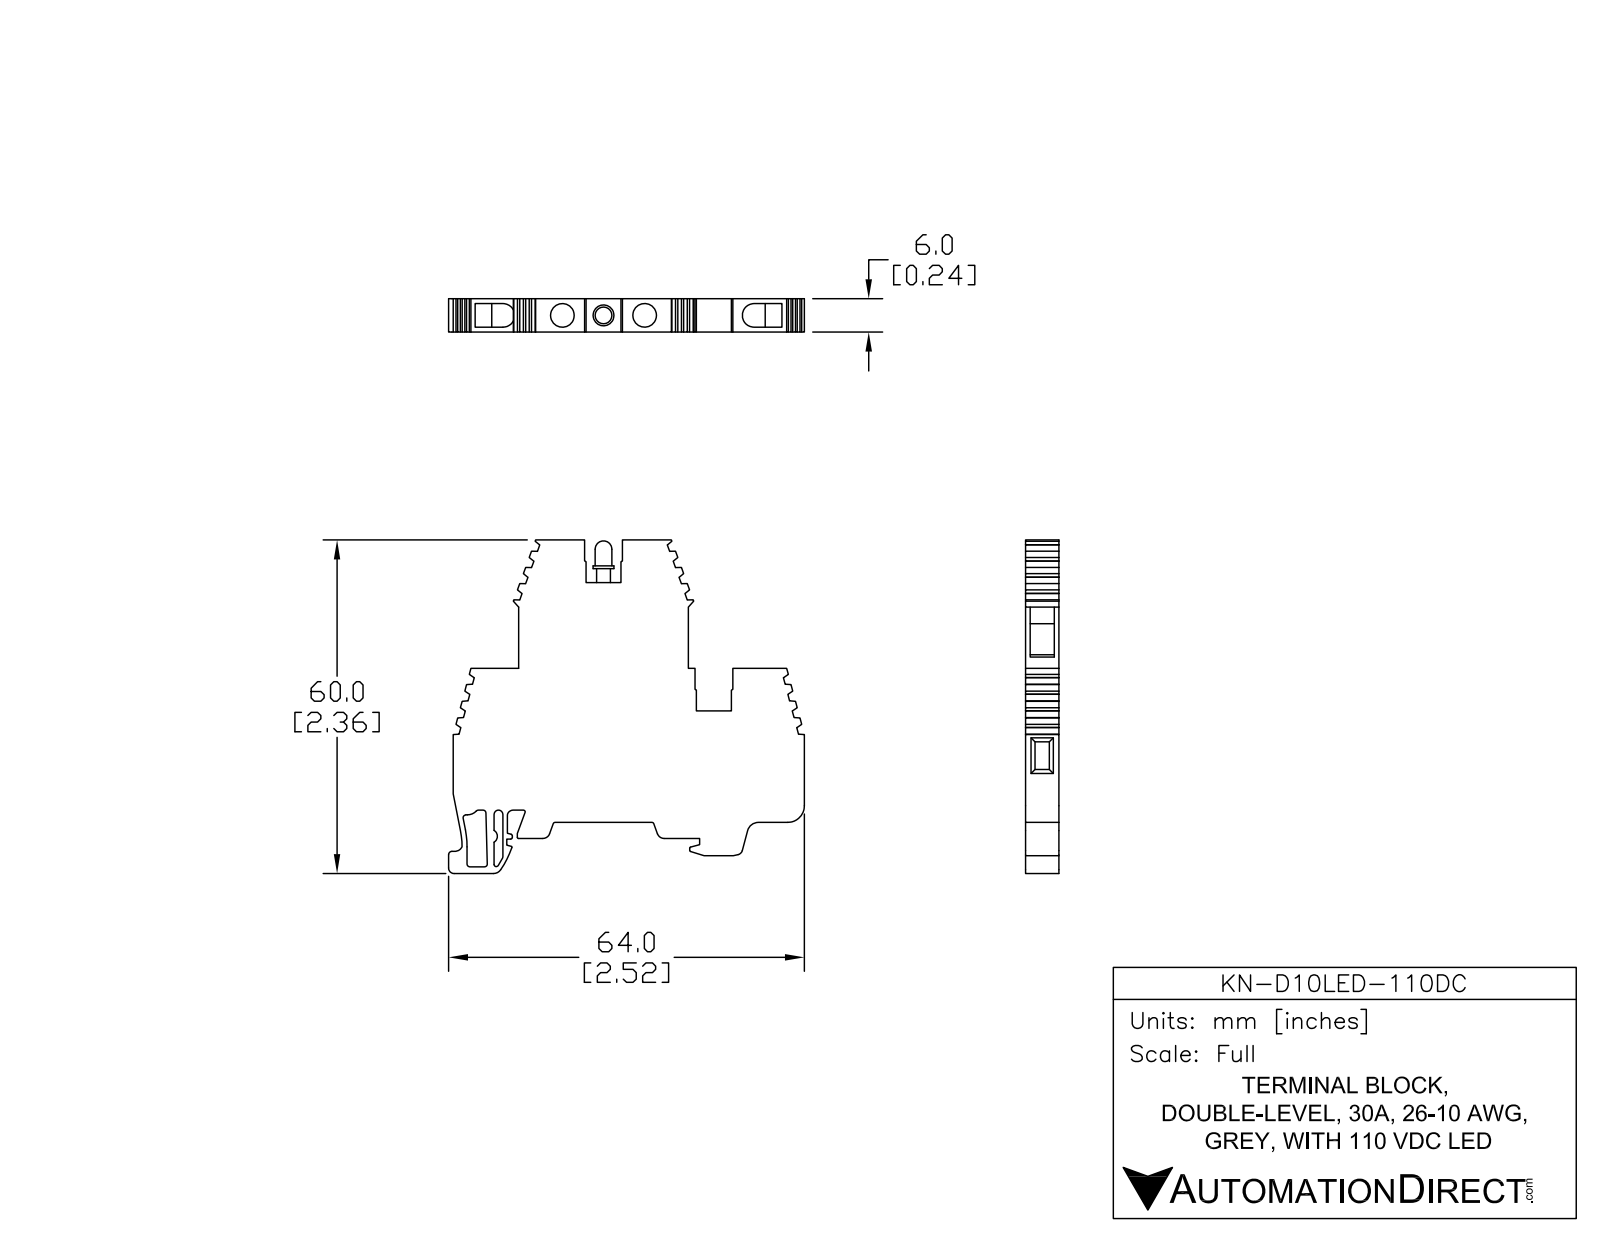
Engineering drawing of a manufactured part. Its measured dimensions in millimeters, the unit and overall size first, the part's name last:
Units: millimetres
Overall size (bounding box): 64.03 × 60 × 6
Round holes (diameter × count): ⌀4.25 ×2
Round bosses / shafts (diameter × count): ⌀3.75 ×1, ⌀3 ×1, ⌀2.5 ×1
Partial cylindrical surfaces — rounded edges, fillets, slot ends (radius × count): R0.5 ×7, R0.3 ×6, R0.2 ×3, R1 ×3, R0.6 ×2, R2.12 ×2, R0.4 ×1, R0.8 ×1
Main face-to-face distances: 6, 5.17, 2.93, 0.83, 23.08, 6.55, 19.86, 6.3, 4, 7.67
Hole centre spacings: 14.8
Volume: 13 705 mm³ · Surface area: 7 525 mm²
Bodies: 3 solids, 246 faces (196 planar, 49 cylindrical, 1 other)
Part name (STEP PRODUCT): KN-D10LED-110DC
STEP written by: SolidWorks 2014 (AUTOMOTIVE_DESIGN)
